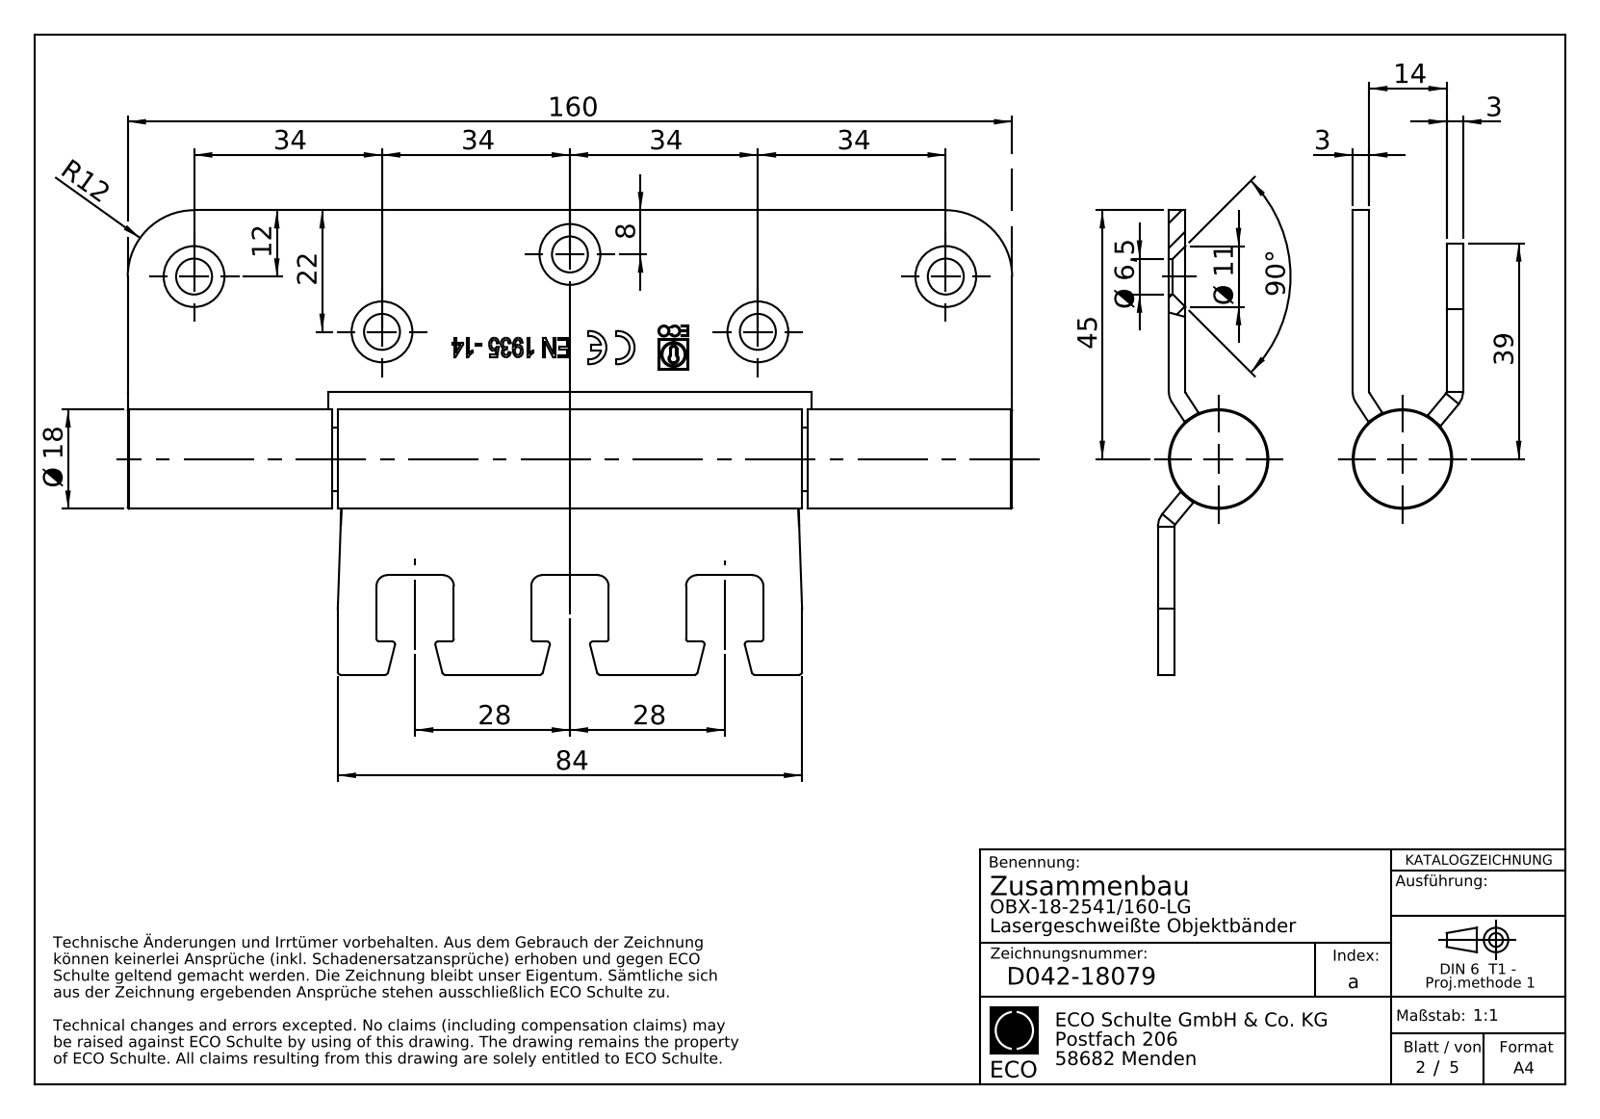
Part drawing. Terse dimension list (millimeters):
name: D044-14308; D046-14312; D043-18083; DIN5401-III (+4 more)
written by: SolidWorks 2017 (AUTOMOTIVE_DESIGN)
unit: mm
bodies: 11 solids, 396 faces (220 planar, 93 cylindrical, 83 other)
size: 160 × 54 × 20
volume: 62 290 mm³; area: 34 277 mm²
holes: 5× ⌀6.5, 2× ⌀2, 1× ⌀0.5, 1× ⌀4.5, 1× ⌀7.9
bosses: 1× ⌀18, 1× ⌀12, 1× ⌀11.8, 1× ⌀11.5, 1× ⌀7.7, 1× ⌀4, 1× ⌀1.65
rounds: 22× R0.5, 6× R0.25, 6× R2, 2× R0.68, 2× R2.1, 2× R3, 2× R3.5, 2× R12
face distances: 3, 17, 20, 14, 122, 38, 11.5, 148.5, 26.5, 110.5
hole spacings: 35.44, 36.77, 68.12, 102.49, 1.95, 4.25, 4.6, 15.05
